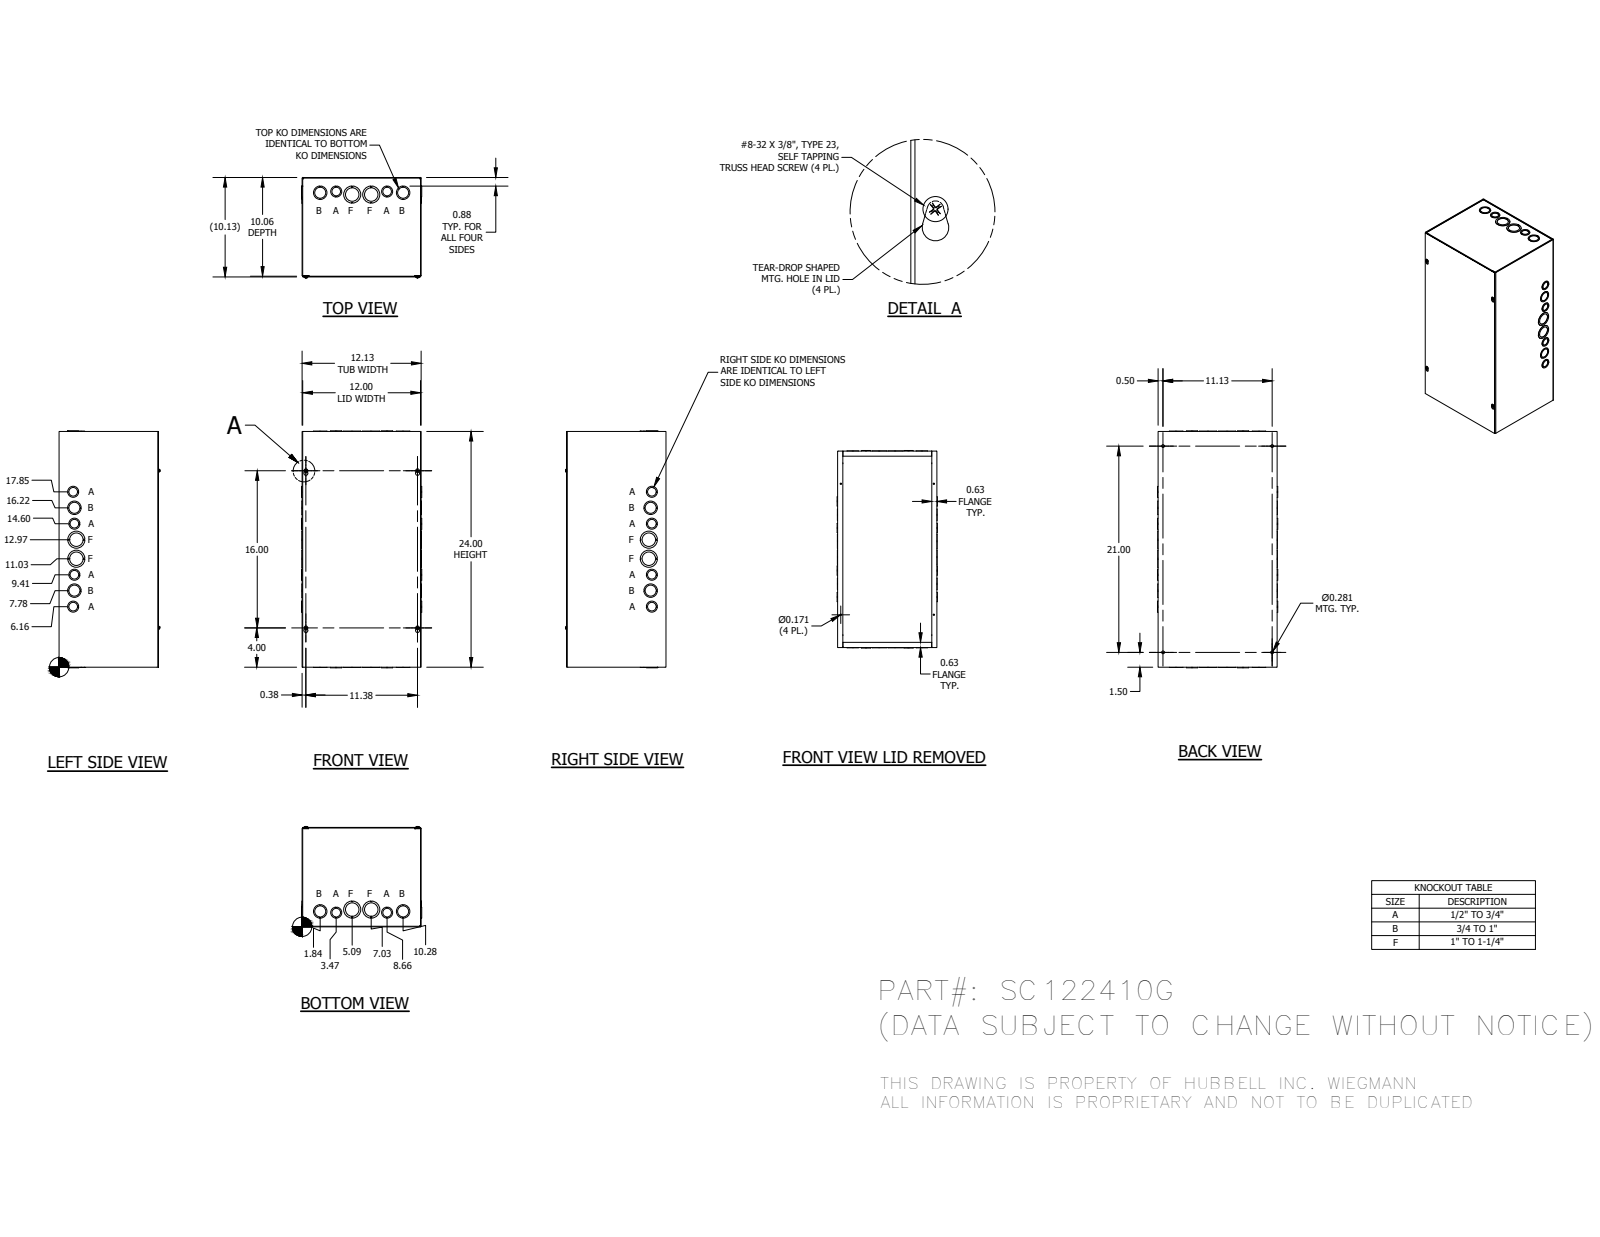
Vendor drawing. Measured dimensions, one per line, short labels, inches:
name: SC122410GBLR; SC1210GTB; SC1224GLPA; 34056 (+1 more)
written by: Autodesk Inventor 2014 (AUTOMOTIVE_DESIGN)
unit: in
bodies: 29 solids, 1055 faces (771 planar, 216 cylindrical, 68 other)
size: 24.125 × 12.25 × 10.225
holes: 12× ⌀1.125, 8× ⌀0.875, 8× ⌀1.375, 4× ⌀0.171, 4× ⌀0.281, 4× ⌀1.75
bosses: 4× ⌀0.384, 4× ⌀0.164
rounds: 12× R0.016, 12× R0.078, 4× R0.125, 4× R0.203
face distances: 0.063, 12.063, 10, 0.062, 10.062, 10.063, 10.125, 12, 12.125, 23.937
hole spacings: 1.63, 1.655, 2.503, 3.256, 3.579, 5.194, 6.816, 11.524
